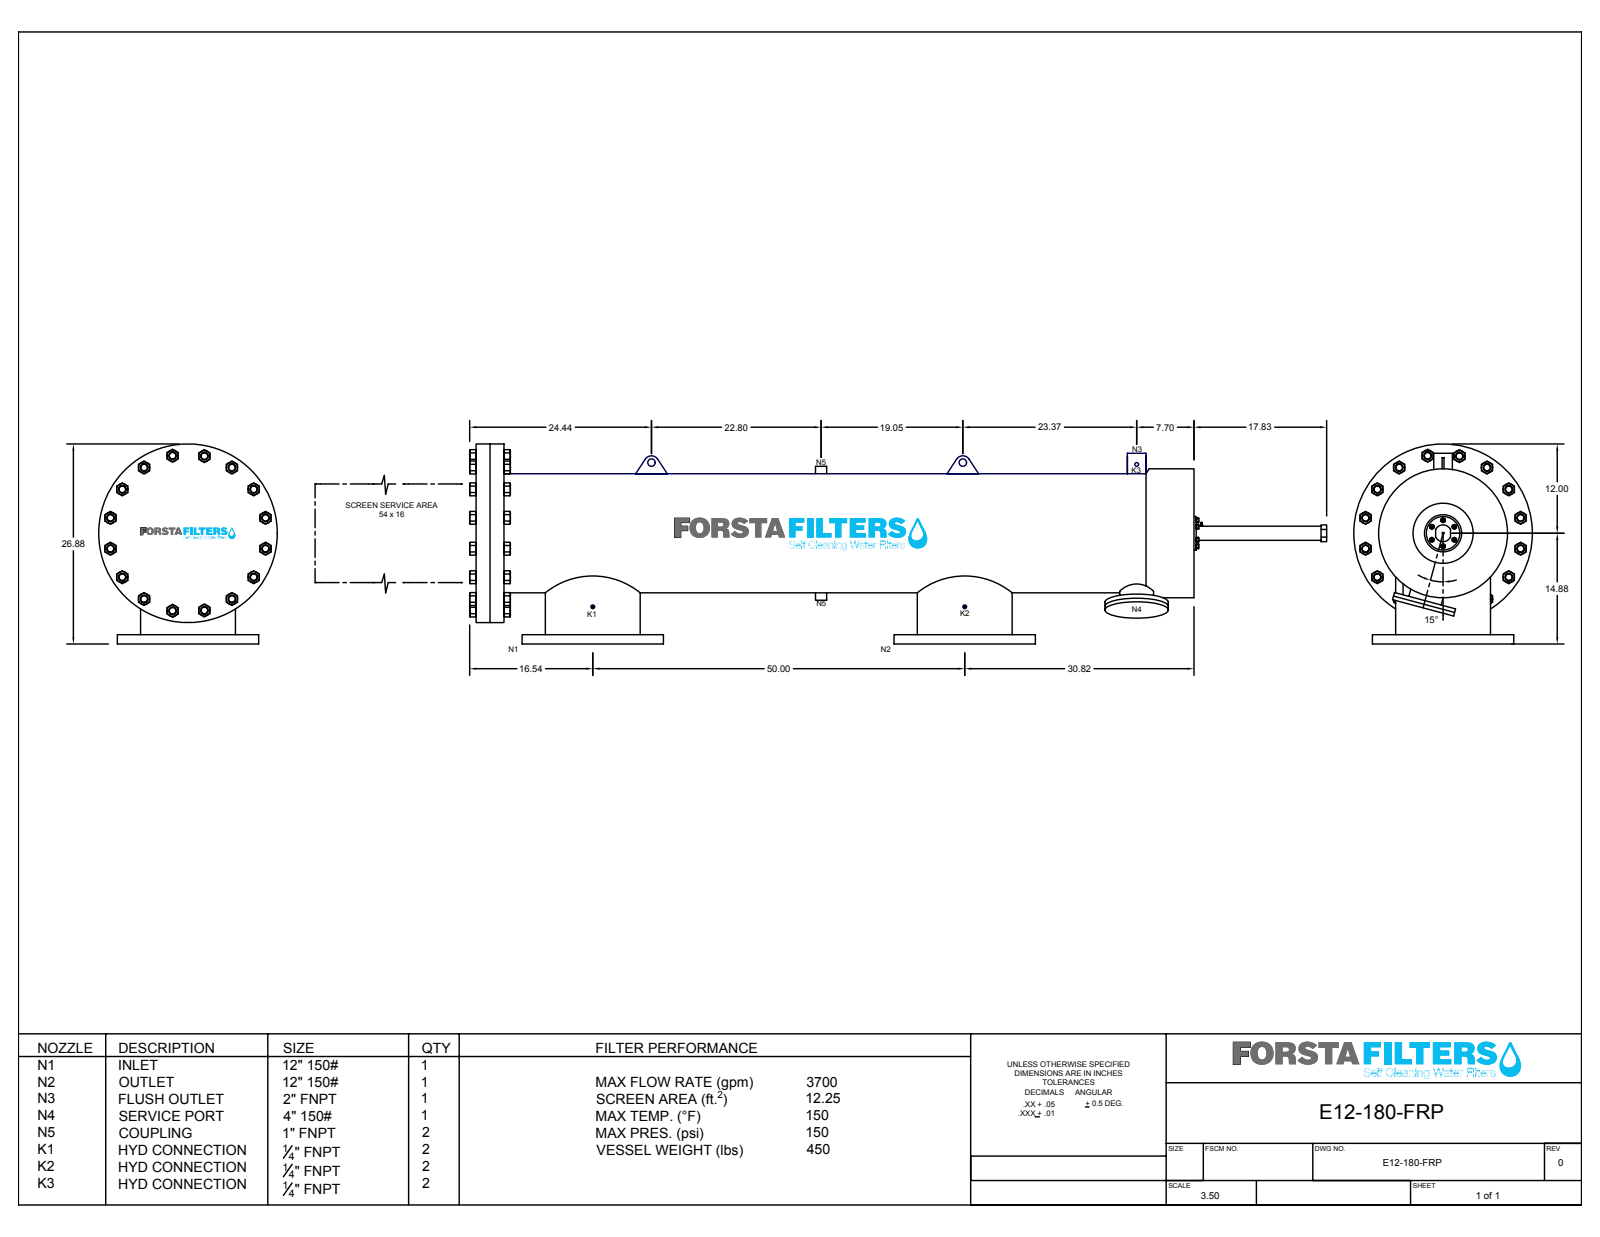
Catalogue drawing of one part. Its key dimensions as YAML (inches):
part_name: "E12-FRP-180"
step_written_by: "SolidWorks 2018 (CONFIG_CONTROL_DESIGN)"
units: inches
bodies: {solids: 22, faces: 742, planar: 380, cylindrical: 354, other: 8}
overall_size: [114.458, 26.88, 24]
volume: 2949
surface_area: 14431
round_holes:
  - {diameter: 1, count: 35}
  - {diameter: 0.75, count: 16}
  - {diameter: 0.38, count: 6}
  - {diameter: 0.25, count: 4}
  - {diameter: 4, count: 2}
  - {diameter: 12, count: 2}
  - {diameter: 1.507, count: 1}
  - {diameter: 2, count: 1}
  - {diameter: 16.934, count: 1}
round_bosses_or_shafts:
  - {diameter: 0.375, count: 4}
  - {diameter: 0.644, count: 3}
  - {diameter: 19, count: 2}
  - {diameter: 12.394, count: 2}
  - {diameter: 9, count: 2}
  - {diameter: 4.394, count: 2}
  - {diameter: 0.375, count: 2}
  - {diameter: 24, count: 1}
partial_cylinders:
  - {radius: 1, count: 2}
  - {radius: 1.126, count: 1}
face_to_face_distances: [1.875, 1.25, 1.875, 3.75, 95.954, 94.079, 92.204, 95.757, 93.882, 92.007]
hole_center_spacings: [2.87, 3.75, 4.146, 5.303, 6.929, 8.132, 8.5, 12.021]
